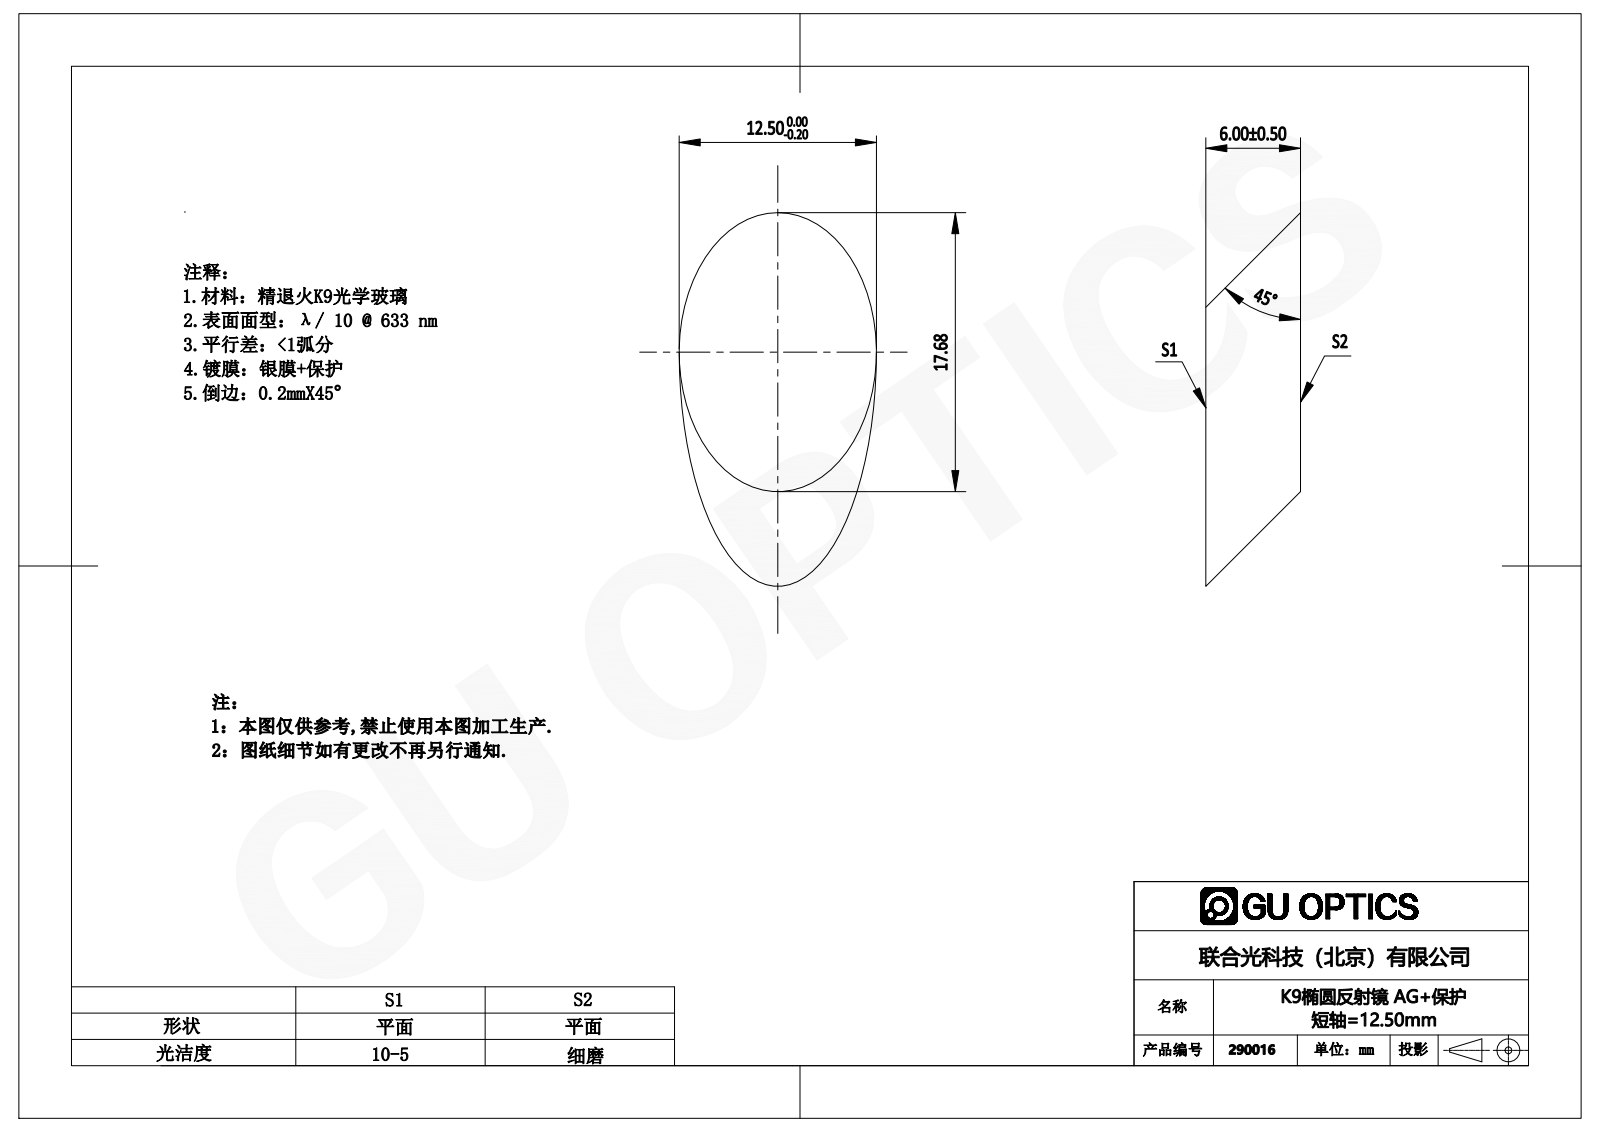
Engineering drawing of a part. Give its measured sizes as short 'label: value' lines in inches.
name: 290000
written by: SolidWorks 2016 (AUTOMOTIVE_DESIGN)
unit: in
bodies: 1 solid, 4 faces (2 planar, 0 cylindrical, 2 other)
size: 0.932 × 0.492 × 0.236
volume: 0.064 in³; area: 1.05 in²
face distances: 0.236
